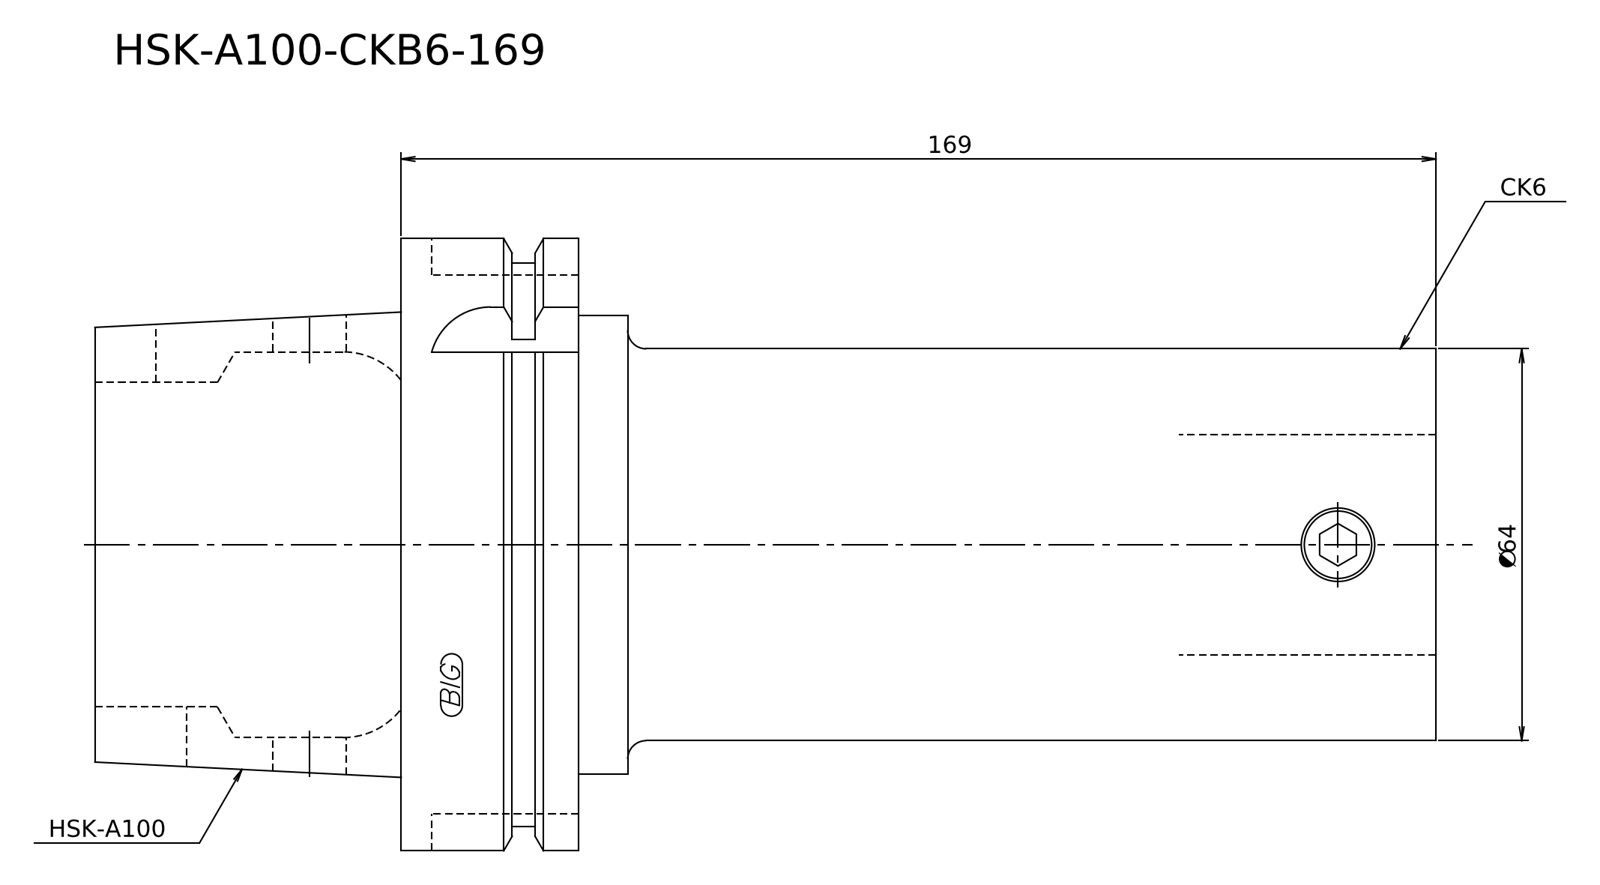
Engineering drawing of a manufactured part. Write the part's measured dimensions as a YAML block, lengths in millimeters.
step_written_by: "Kubotek KeyCreator V8.5.1 (14335) (CONFIG_CONTROL_DESIGN)"
units: millimeters
bodies: {solids: 1, faces: 17, planar: 7, cylindrical: 6, other: 4}
overall_size: [219, 100, 100]
volume: 895355
surface_area: 65589
round_bosses_or_shafts:
  - {diameter: 100, count: 1}
  - {diameter: 92, count: 1}
  - {diameter: 75.8, count: 1}
  - {diameter: 75, count: 1}
  - {diameter: 64, count: 1}
face_to_face_distances: [79, 29, 50, 140, 169, 219, 132, 8, 37, 87]
